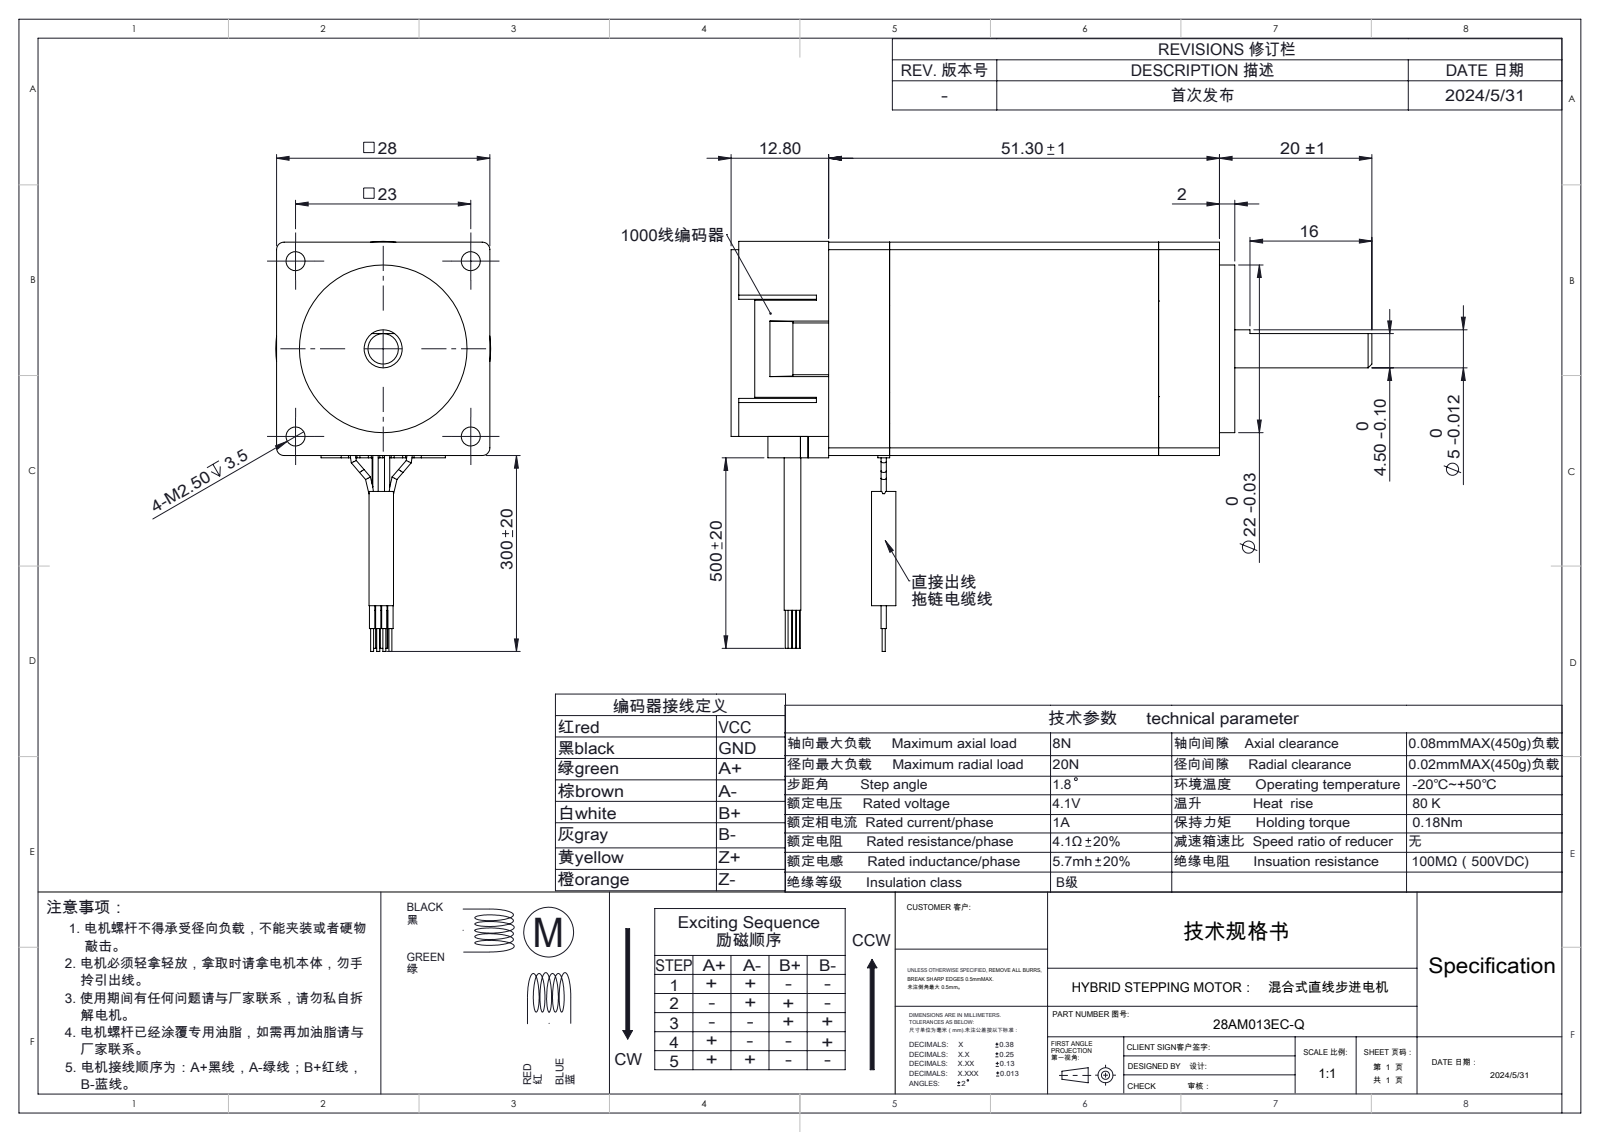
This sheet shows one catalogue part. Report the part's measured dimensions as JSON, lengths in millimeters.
{"part_name": "28AM013EC", "step_written_by": "SolidWorks 2024 (AUTOMOTIVE_DESIGN)", "units": "millimeters", "bodies": {"solids": 7, "faces": 515, "planar": 380, "cylindrical": 113, "other": 22}, "overall_size": [84.1, 53.8, 28.2], "volume_mm3": 47218, "surface_area_mm2": 16725, "round_holes": [[0.55, 6], [2.5, 4], [5, 1], [10.9, 1]], "round_bosses_or_shafts": [[0.46, 8], [0.7, 6], [0.4, 4], [28.2, 1], [26, 1], [22, 1], [12.55, 1], [11.45, 1]], "partial_cylinders_radius": [[0.2, 4], [1, 4], [13.15, 1]], "face_to_face_distances": [28, 8, 43.3, 35.3, 12.8, 20.8, 56.1, 2, 10, 53.3], "hole_center_spacings": [1.5, 3, 16.26, 23, 4.5, 6, 32.53, 7.5]}
